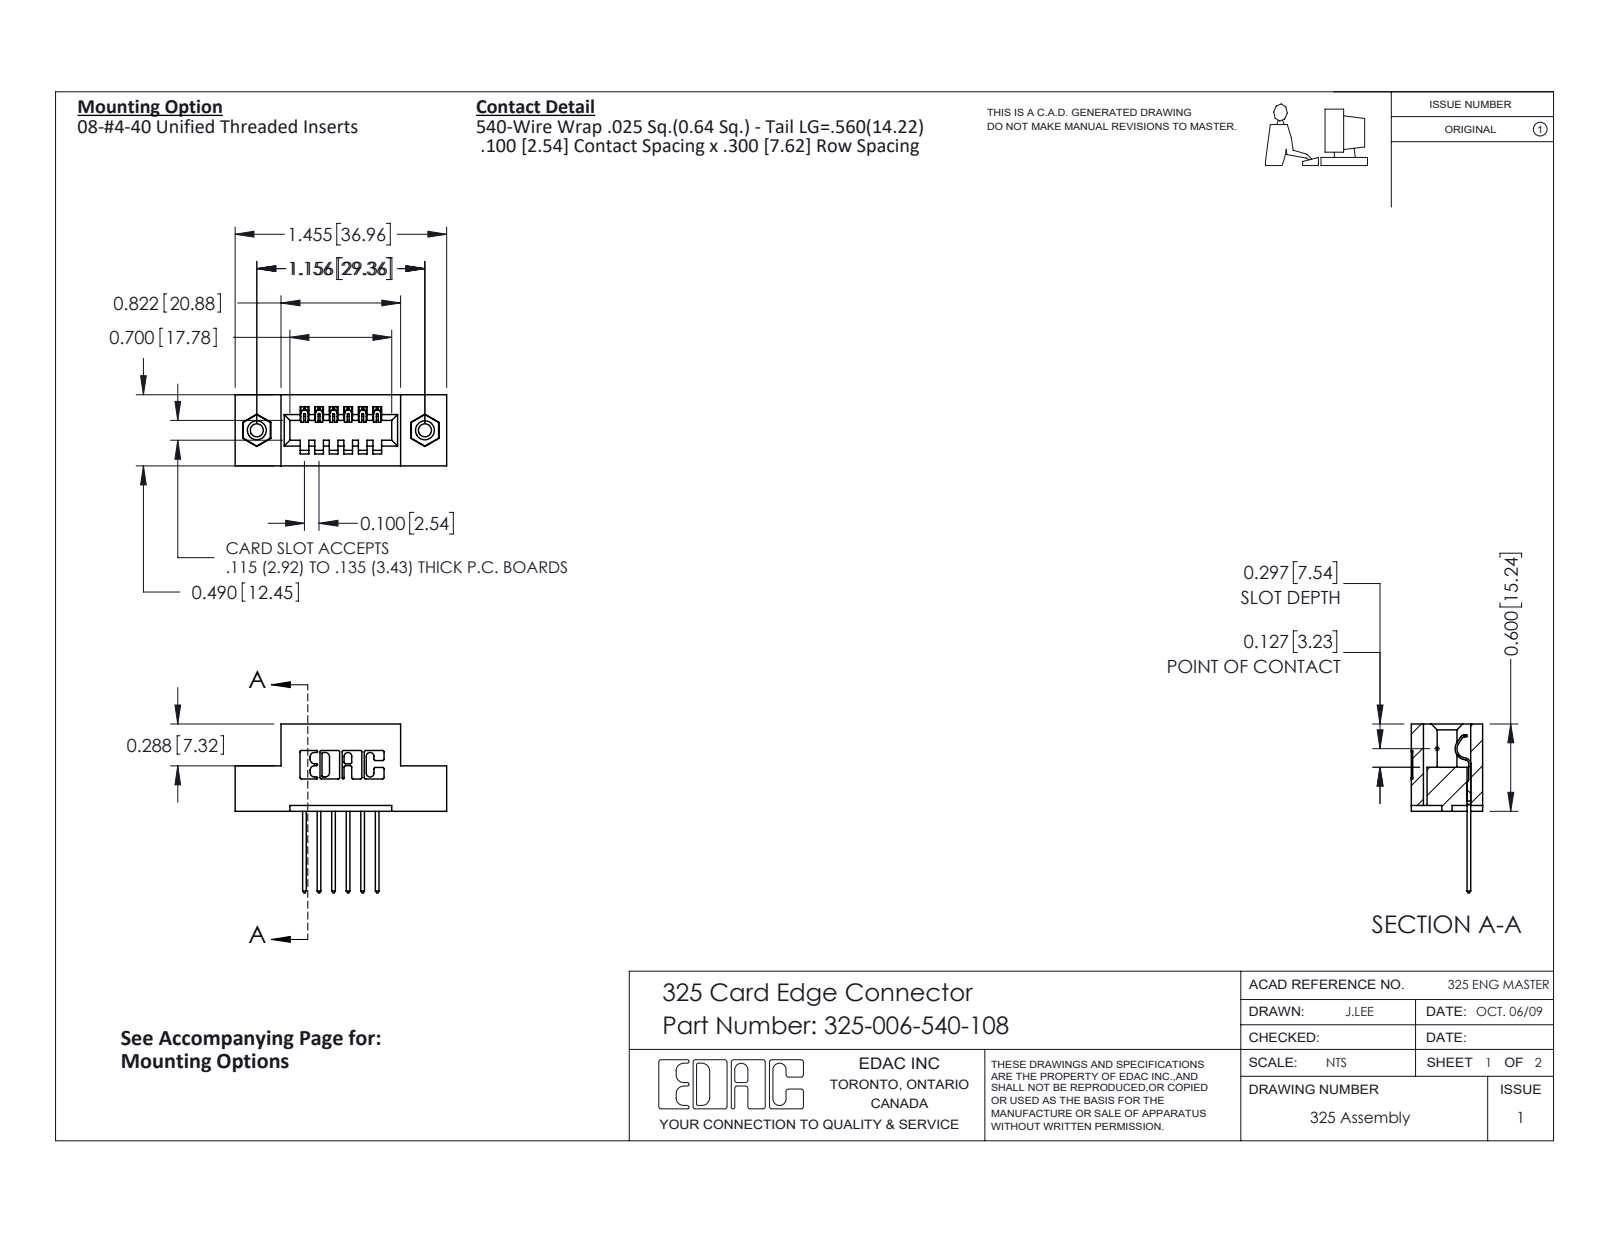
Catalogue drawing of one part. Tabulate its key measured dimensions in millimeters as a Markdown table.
| quantity | value |
| --- | --- |
| part name | 345-250-001_345-250-003-102; 325-292-001_325-293-140; 325 Part_TI; 325-006-540-108 |
| STEP written by | SolidWorks 2016 (CONFIG_CONTROL_DESIGN) |
| units | millimeters |
| bodies | 9 solids, 522 faces (354 planar, 152 cylindrical, 16 other) |
| overall size | 37 × 29.5 × 12.4 |
| volume | 4 410 mm³ |
| surface area | 4 283 mm² |
| round holes (diameter × count) | 2.3 × 2, 3.2 × 2, 4.1 × 2 |
| round bosses / shafts (diameter × count) | 3.9 × 2 |
| partial cylindrical surfaces (radius × count) | 0.3 × 22, 0.2 × 12, 0.3 × 12, 0.2 × 6, 0.8 × 6, 0.7 × 3, 0.4 × 1, 0.6 × 1 |
| main face-to-face distances | 7.6, 2.5, 1, 2.1, 12.4, 5.1, 10.3, 1.5, 9.7, 4.1 |
| hole center spacings | 29.4 |
